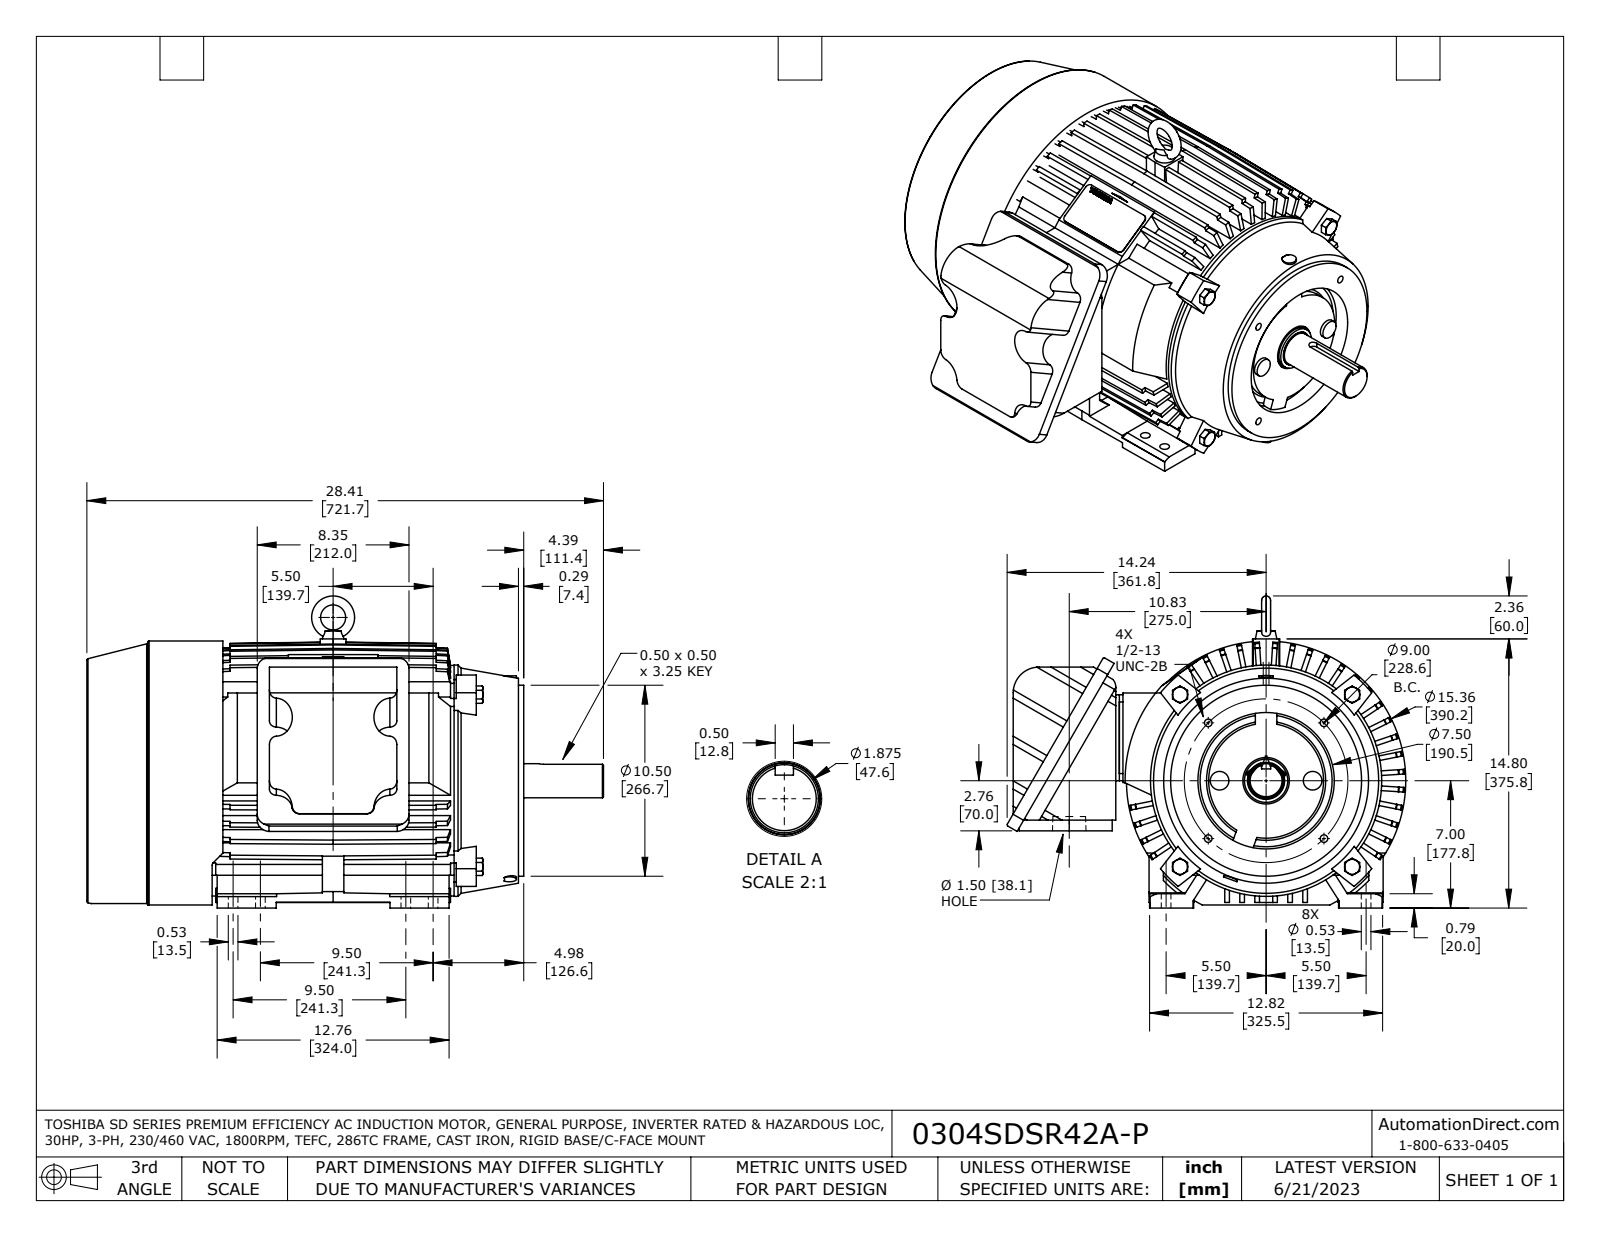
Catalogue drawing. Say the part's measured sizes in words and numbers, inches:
The part is named "MDSLV005-05-F1-Bottom nc bod broke rep1". Its 3-D file was written by "SolidWorks 2021 (AUTOMOTIVE_DESIGN)". It is 13 solids with 2701 faces: 2147 planar, 272 cylindrical and 282 other. Overall it measures 28.413 by 21.924 by 17.157 inches. Its volume is 4 162 cubic inches and its surface area 3 901 square inches. Round holes: 8 of diameter 0.354, 8 of diameter 0.531, 4 of diameter 0.087, 4 of diameter 0.398, 4 of diameter 0.417, 4 of diameter 0.551, 1 of diameter 0.472, 1 of diameter 0.545, 1 of diameter 0.827, 1 of diameter 1.988, 1 of diameter 2.004, 1 of diameter 2.559. Round bosses or shafts: 2 of diameter 1.024, 1 of diameter 15.362, 1 of diameter 12.717, 1 of diameter 12.677, 1 of diameter 12.244, 1 of diameter 10.5, 1 of diameter 6.319, 1 of diameter 2.756. Partial cylindrical surfaces (rounded edges, fillets, slot ends): 27 of radius 0.394, 6 of radius 0.021, 6 of radius 0.042, 6 of radius 0.055, 6 of radius 0.906, 4 of radius 0.02, 4 of radius 0.09, 4 of radius 0.25. The main face-to-face distances are 0.591, 13.307, 12.717, 0.256, 13.024, 12.433, 0.283, 0.255, 6.89, 0.197. The hole center spacings are 7.661, 8.065, 9.124, 11, 0.492, 1.5, 1.701, 2.193.
